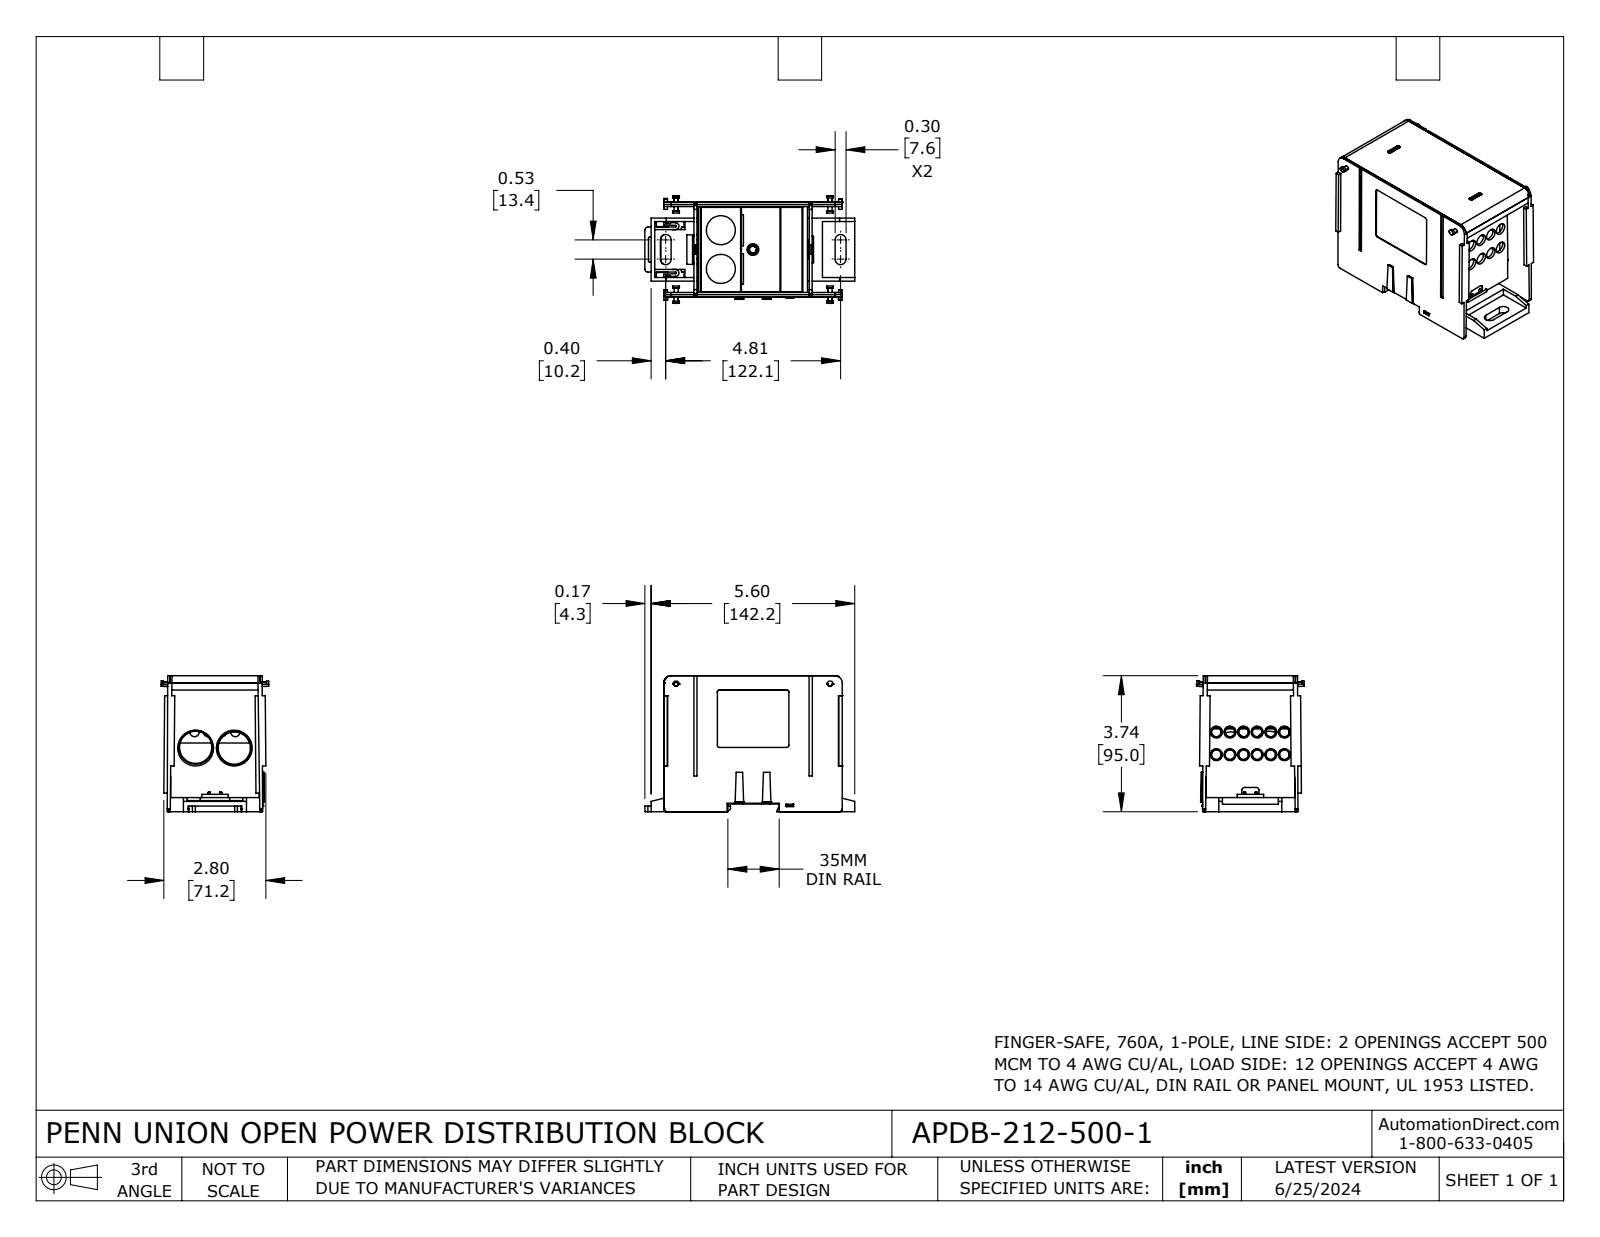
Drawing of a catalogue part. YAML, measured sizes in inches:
part_name: "APDB-212-500-1"
step_written_by: "SolidWorks 2023 (CONFIG_CONTROL_DESIGN)"
units: inches
bodies: {solids: 16, faces: 910, planar: 584, cylindrical: 209, other: 117}
overall_size: [5.77, 3.741, 2.955]
volume: 19.34
surface_area: 237.3
round_holes:
  - {diameter: 0.256, count: 12}
  - {diameter: 0.327, count: 12}
  - {diameter: 0.798, count: 2}
  - {diameter: 0.886, count: 2}
  - {diameter: 0.984, count: 2}
  - {diameter: 0.213, count: 1}
  - {diameter: 0.28, count: 1}
partial_cylinders:
  - {radius: 0.02, count: 30}
  - {radius: 0.059, count: 18}
  - {radius: 0.039, count: 10}
  - {radius: 0.079, count: 10}
  - {radius: 0.197, count: 10}
  - {radius: 0.012, count: 6}
  - {radius: 0.089, count: 4}
  - {radius: 0.15, count: 4}
face_to_face_distances: [0.079, 3.169, 2.54, 0.071, 2.469, 0.02, 3.248, 0.089, 3.091, 1.201]
hole_center_spacings: [0.374, 0.726, 0.748, 0.973, 0.622, 1.122, 1.283, 0.442]
